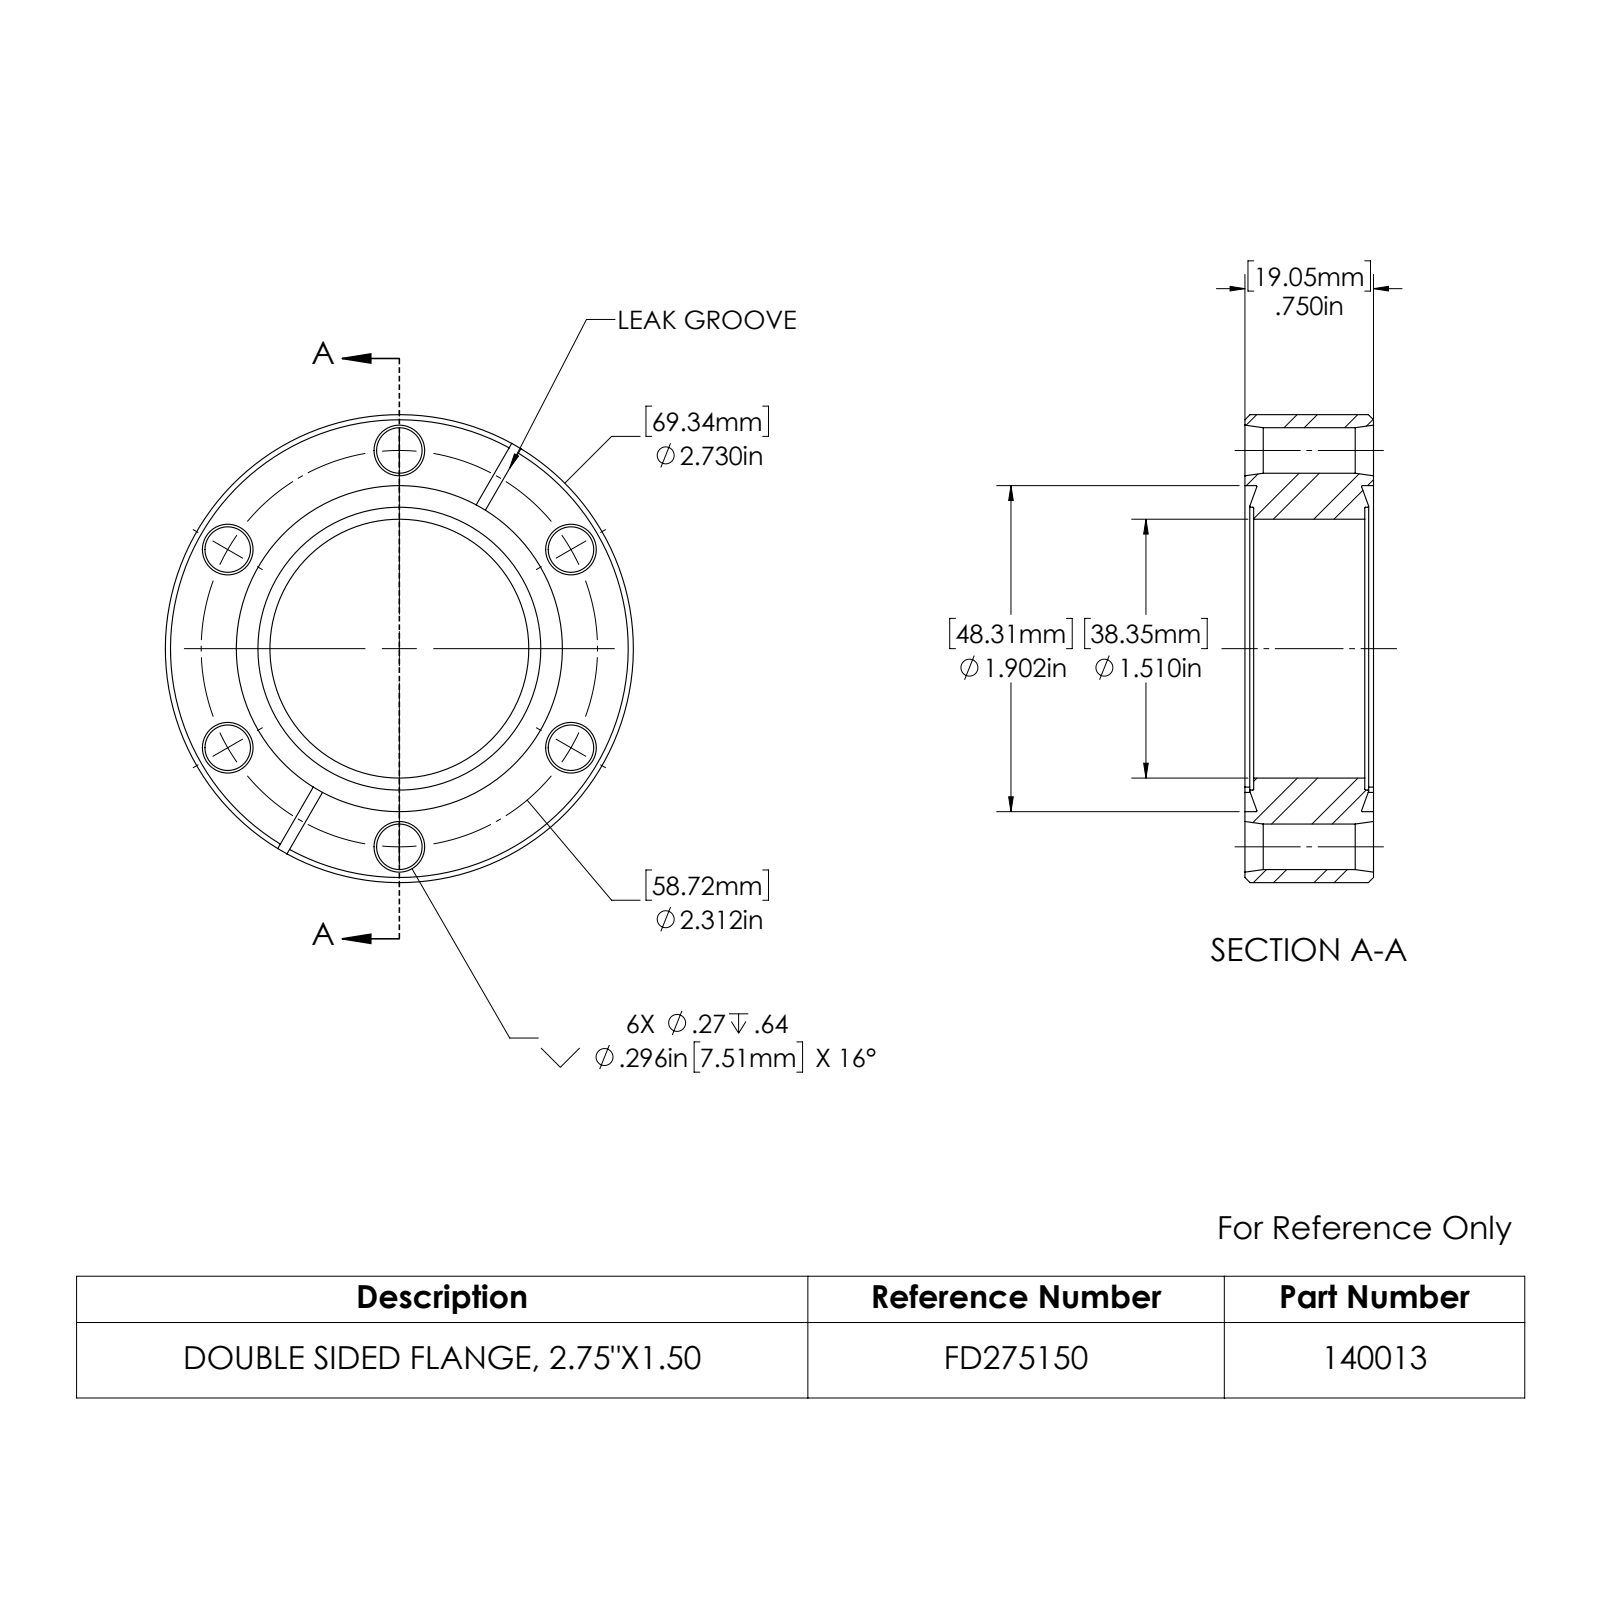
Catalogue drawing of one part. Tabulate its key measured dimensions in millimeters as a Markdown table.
| quantity | value |
| --- | --- |
| part name | 140013_A |
| STEP written by | SolidWorks 2022 (CONFIG_CONTROL_DESIGN) |
| units | millimeters |
| bodies | 1 solid, 88 faces (14 planar, 28 cylindrical, 46 other) |
| overall size | 69.3 × 69.3 × 19.1 |
| volume | 43 690 mm³ |
| surface area | 14 020 mm² |
| round holes (diameter × count) | 6.8 × 6, 38.4 × 1, 41.9 × 1, 48.3 × 1 |
| round bosses / shafts (diameter × count) | 69.3 × 1 |
| partial cylindrical surfaces (radius × count) | 31.8 × 4 |
| main face-to-face distances | 19.1, 1.3, 17.8, 16.5, 1.6 |
| hole center spacings | 29.4, 50.9, 50.9, 58.7, 58.7 |
